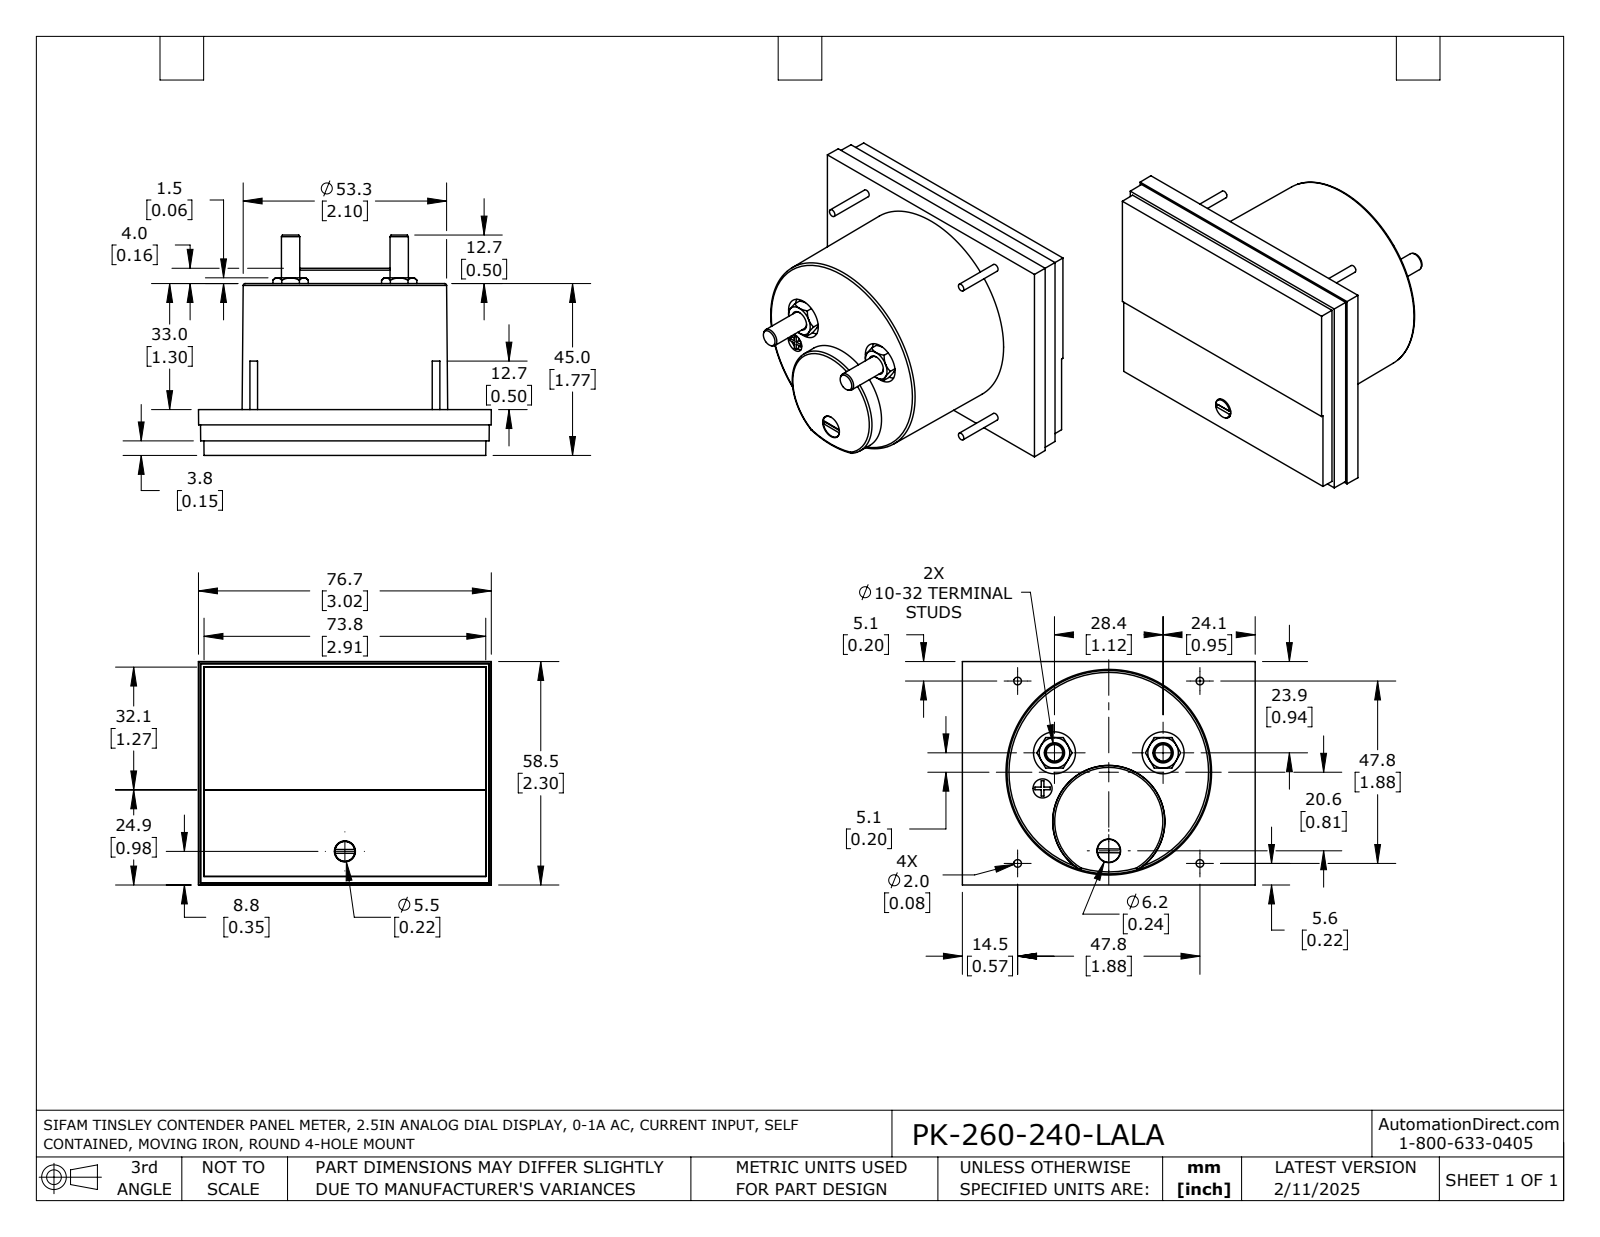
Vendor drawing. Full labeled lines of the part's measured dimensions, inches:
Part name (STEP PRODUCT): PK-260-240-LALA
STEP written by: SolidWorks 2021 (AUTOMOTIVE_DESIGN)
Units: inches
Bodies: 1 solid, 192 faces (95 planar, 37 cylindrical, 60 other)
Overall size (bounding box): 3.02 × 2.303 × 2.272
Volume: 7.657 in³ · Surface area: 36.55 in²
Round holes (diameter × count): ⌀0.197 ×3, ⌀0.433 ×2, ⌀0.209 ×1, ⌀0.217 ×1, ⌀0.244 ×1
Round bosses / shafts (diameter × count): ⌀0.079 ×4, ⌀0.189 ×2, ⌀0.236 ×1, ⌀0.205 ×1
Partial cylindrical surfaces — rounded edges, fillets, slot ends (radius × count): R0.033 ×1
Main face-to-face distances: 0.02, 0.472, 0.13, 0.322, 0.15, 0.453, 0.057, 0.077, 0.396, 0.073
Hole centre spacings: 1.155, 1.16, 0.387, 0.938, 0.942, 1.12, 1.295
